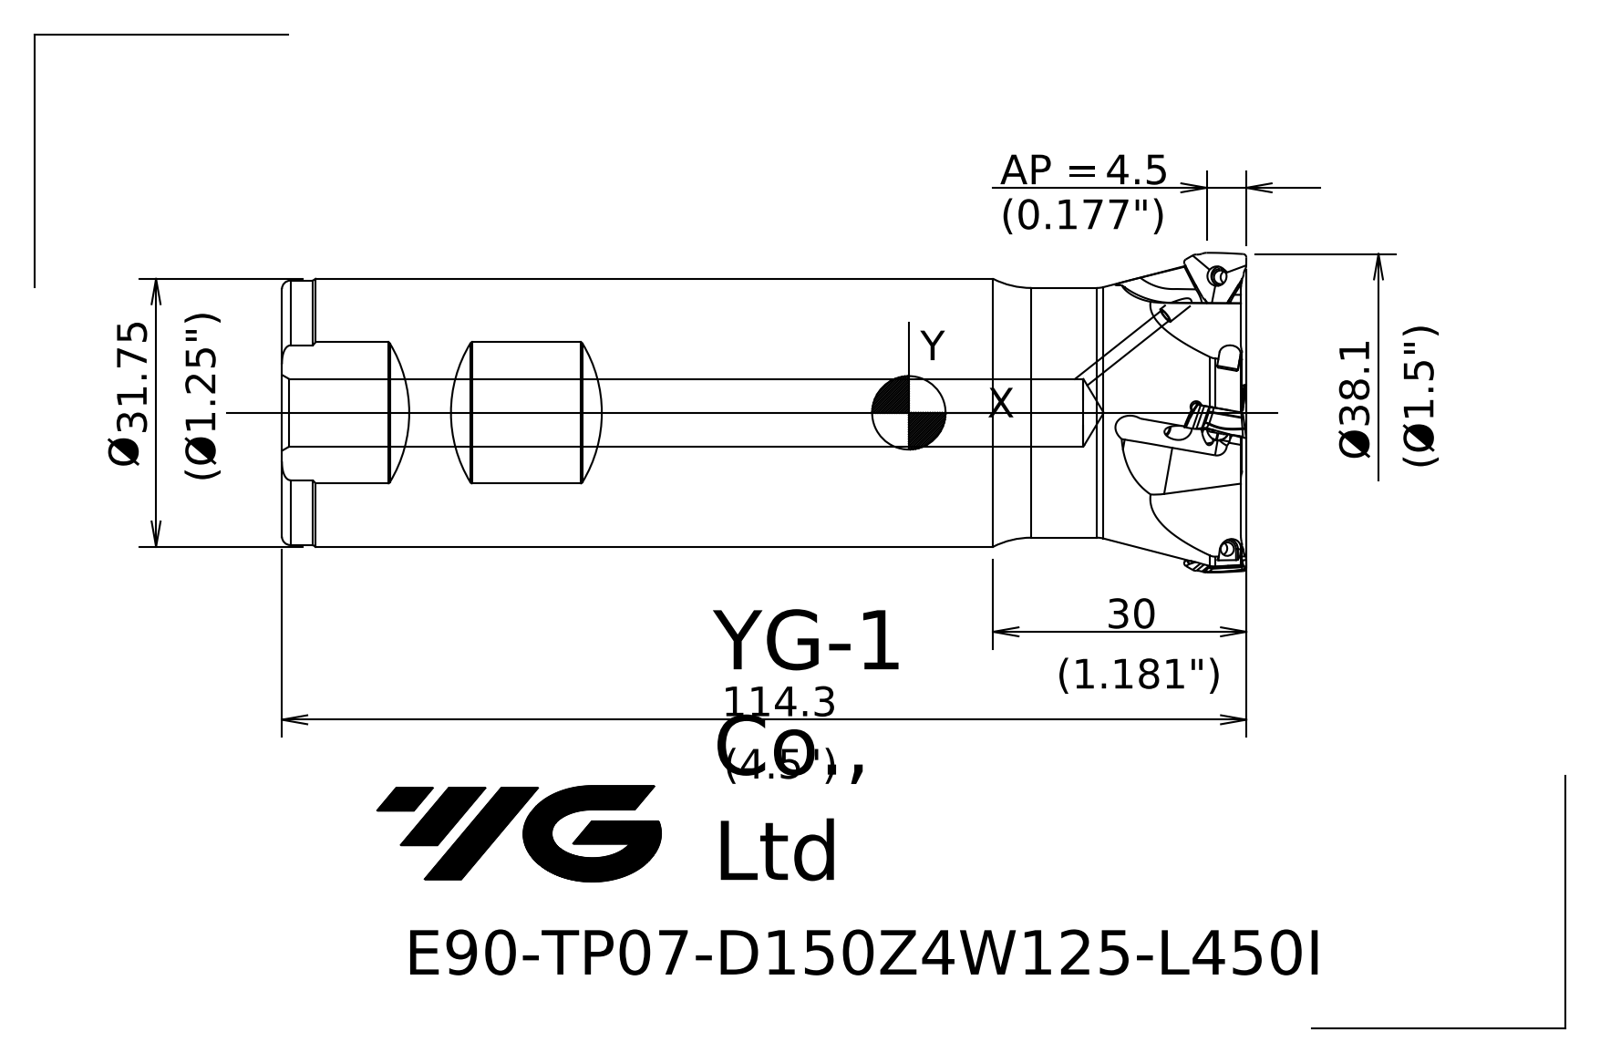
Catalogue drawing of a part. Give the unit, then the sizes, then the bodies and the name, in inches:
Units: inches
Overall size (bounding box): 4.5 × 1.502 × 1.502
Round holes (diameter × count): ⌀0.059 ×1, ⌀0.315 ×1
Round bosses / shafts (diameter × count): ⌀1.25 ×1, ⌀1.234 ×1, ⌀1.165 ×1
Partial cylindrical surfaces — rounded edges, fillets, slot ends (radius × count): R0.012 ×3
Main face-to-face distances: 4.474, 4.48, 0.635
Volume: 5.179 in³ · Surface area: 27.76 in²
Bodies: 1 solid, 51 faces (8 planar, 8 cylindrical, 35 other)
Part name (STEP PRODUCT): 10221A00A9E9z338
STEP written by: SIEMENS PLM Software NX 10.0 (AP203_CONFIGURATION_CONTROLLED_3D_DESIGN_OF_MECHANICAL_PARTS_AND_ASSEMBLIES_MIM_LF)
